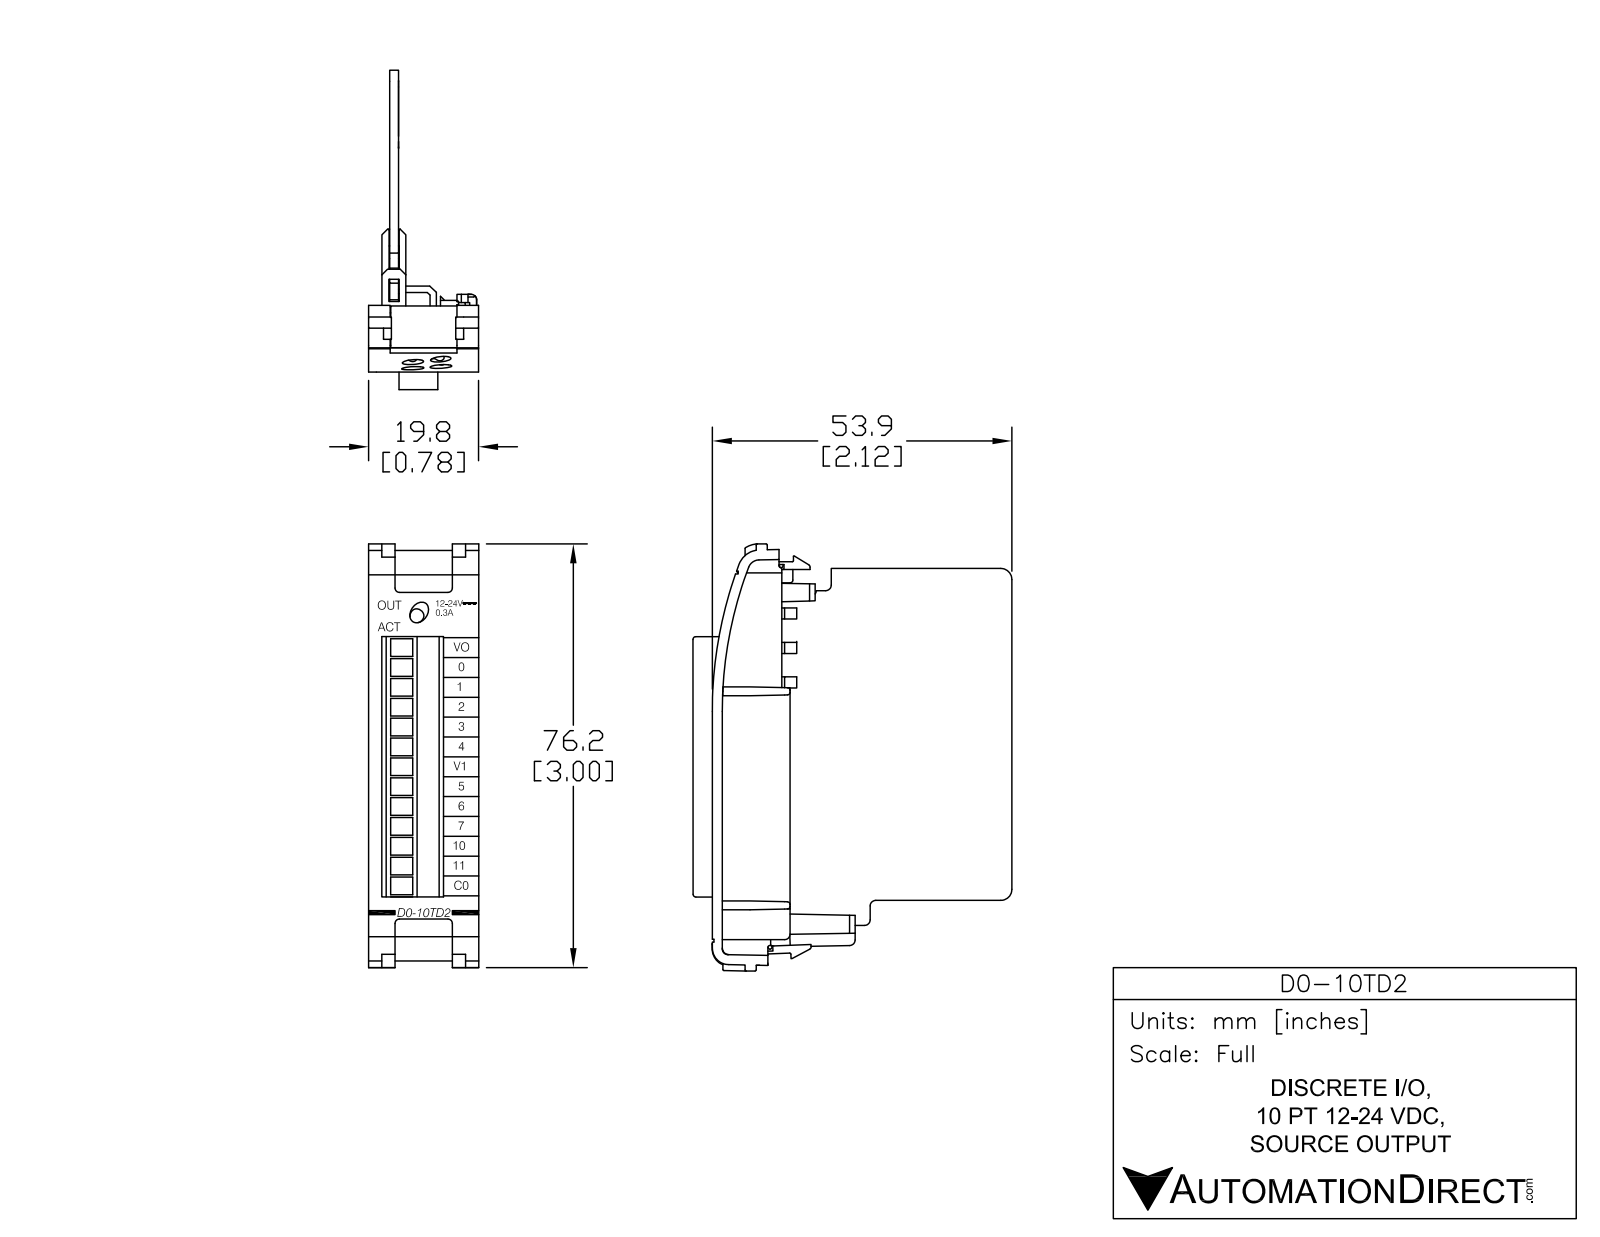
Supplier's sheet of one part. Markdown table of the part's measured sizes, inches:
| quantity | value |
| --- | --- |
| part name | D0-10TD2 |
| STEP written by | SolidWorks 2009 (AUTOMOTIVE_DESIGN) |
| units | inches |
| bodies | 2 solids, 357 faces (279 planar, 38 cylindrical, 40 other) |
| overall size | 3.08 × 2.542 × 0.826 |
| volume | 0.753 in³ |
| surface area | 24.14 in² |
| round bosses / shafts (diameter × count) | 0.08 × 1 |
| partial cylindrical surfaces (radius × count) | 0.005 × 4, 0.02 × 3, 0.035 × 3, 0.025 × 2, 0.01 × 1, 0.065 × 1, 0.07 × 1, 0.1 × 1 |
| main face-to-face distances | 0.063, 0.05, 0.631, 0.075, 0.113, 0.581, 0.518, 0.681, 0.568, 0.06 |
